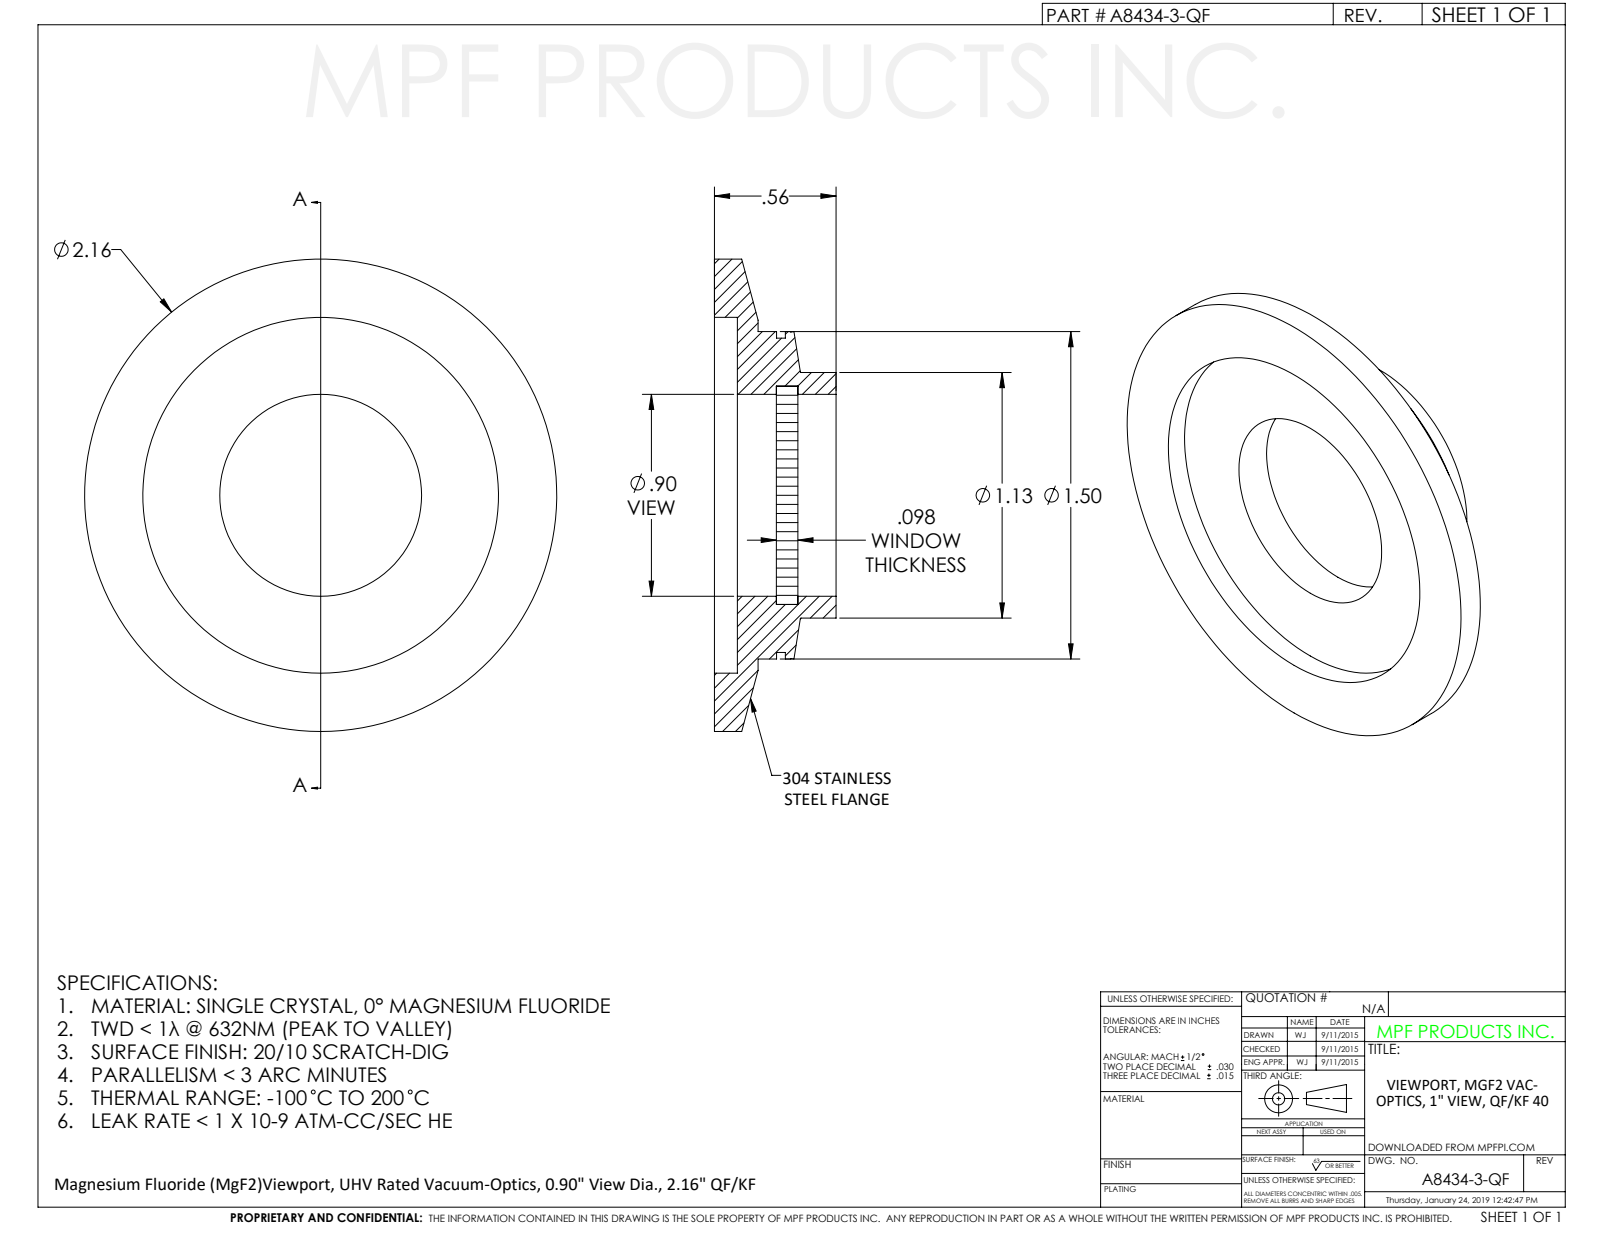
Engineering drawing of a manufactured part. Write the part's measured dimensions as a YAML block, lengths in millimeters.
part_name: "A8434-3-QF"
step_written_by: "SolidWorks 2012 (CONFIG_CONTROL_DESIGN)"
units: millimeters
bodies: {solids: 1, faces: 37, planar: 9, cylindrical: 16, other: 12}
overall_size: [55, 55, 14.1]
volume: 11600
surface_area: 7374
round_holes:
  - {diameter: 23.5, count: 1}
  - {diameter: 41.4, count: 1}
round_bosses_or_shafts:
  - {diameter: 55, count: 1}
  - {diameter: 38.1, count: 1}
  - {diameter: 36.6, count: 1}
  - {diameter: 28.6, count: 1}
face_to_face_distances: [2.7, 7.2, 9.7, 4.5, 7, 2.5, 14.1, 11.5, 7, 4.4]
